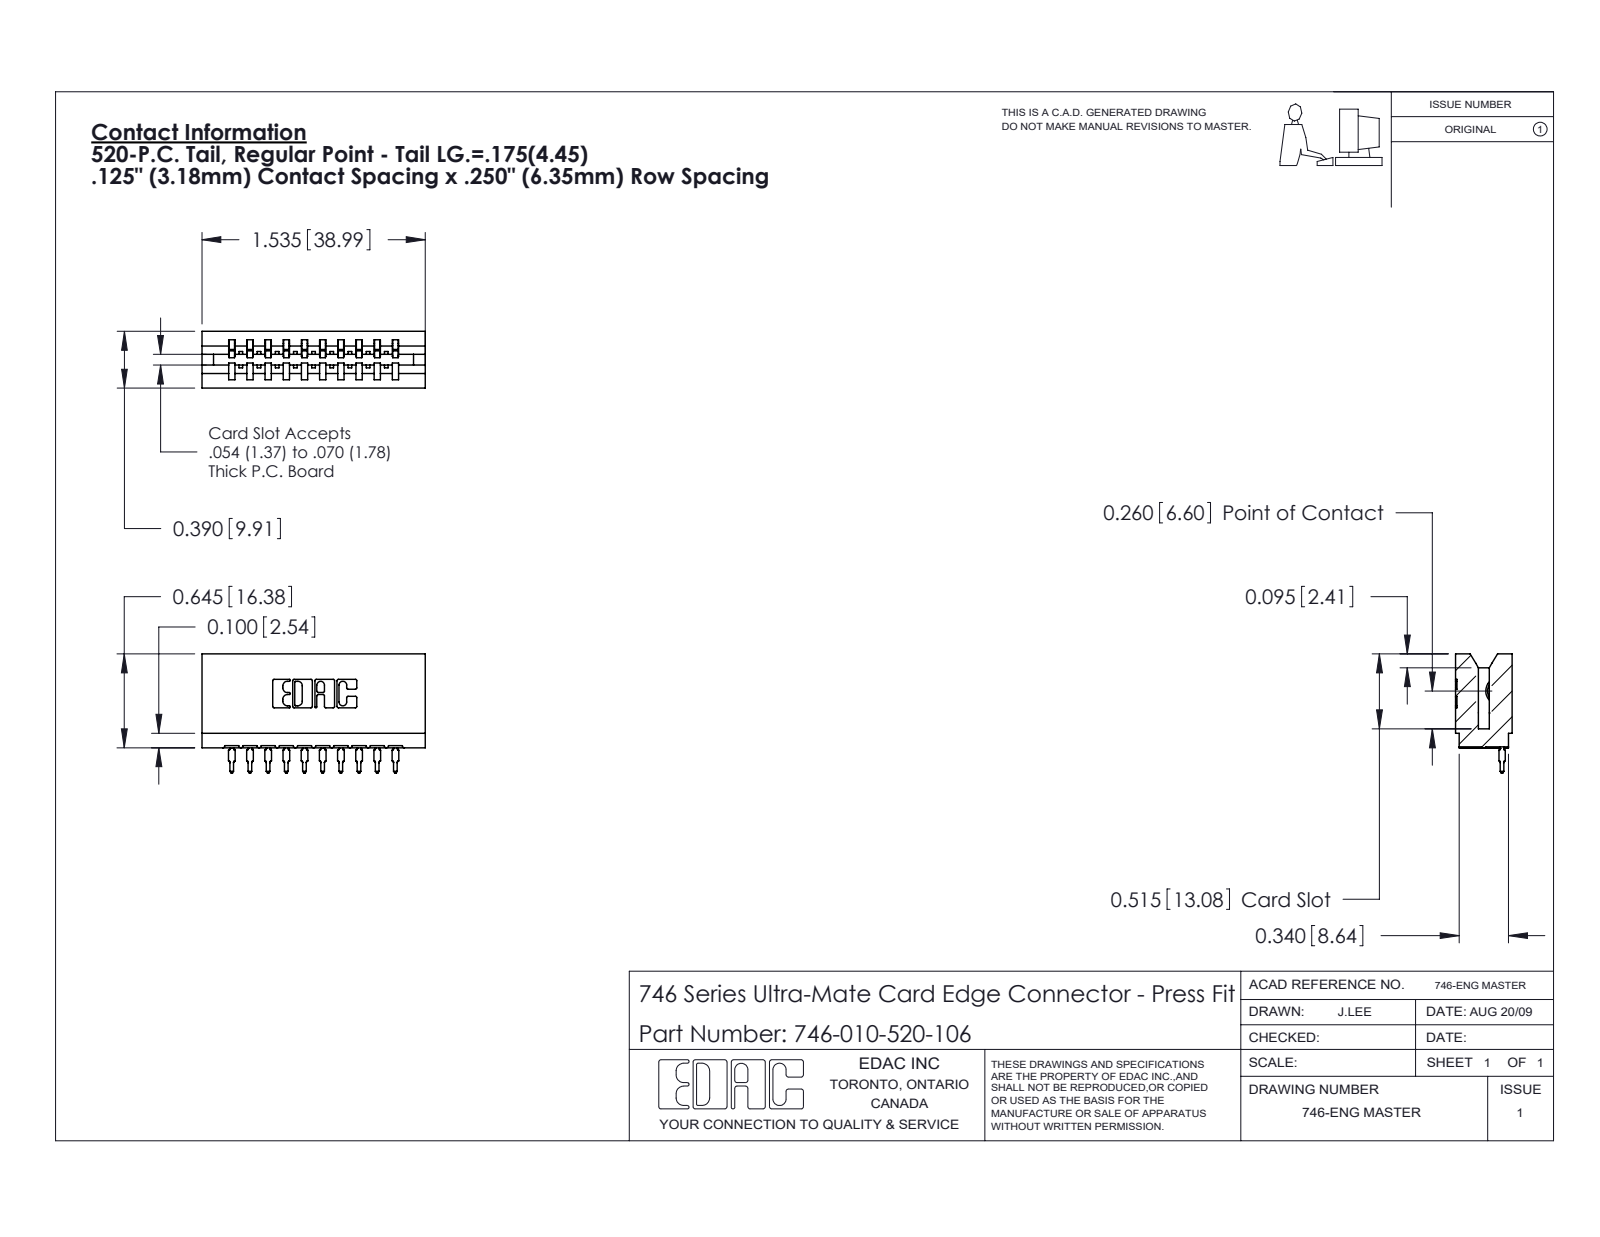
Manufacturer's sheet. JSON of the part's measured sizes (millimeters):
{"part_name": "746 Part_.515 Slot Depth - 06; 746-292-001_520; 746-010-520-106", "step_written_by": "SolidWorks 2020 (CONFIG_CONTROL_DESIGN)", "units": "millimeters", "bodies": {"solids": 11, "faces": 1178, "planar": 686, "cylindrical": 232, "other": 260}, "overall_size": [39, 20.8, 9.9], "volume_mm3": 4260, "surface_area_mm2": 5712, "partial_cylinders_radius": [[0.3, 22], [0.5, 20], [0.4, 11], [0.2, 6], [0.8, 6], [0.1, 4], [0.3, 4], [0.7, 3]], "face_to_face_distances": [6.4, 12.7, 8.5, 1.1, 3.2, 1.4, 7.4, 19.1, 9.9, 9.5]}
